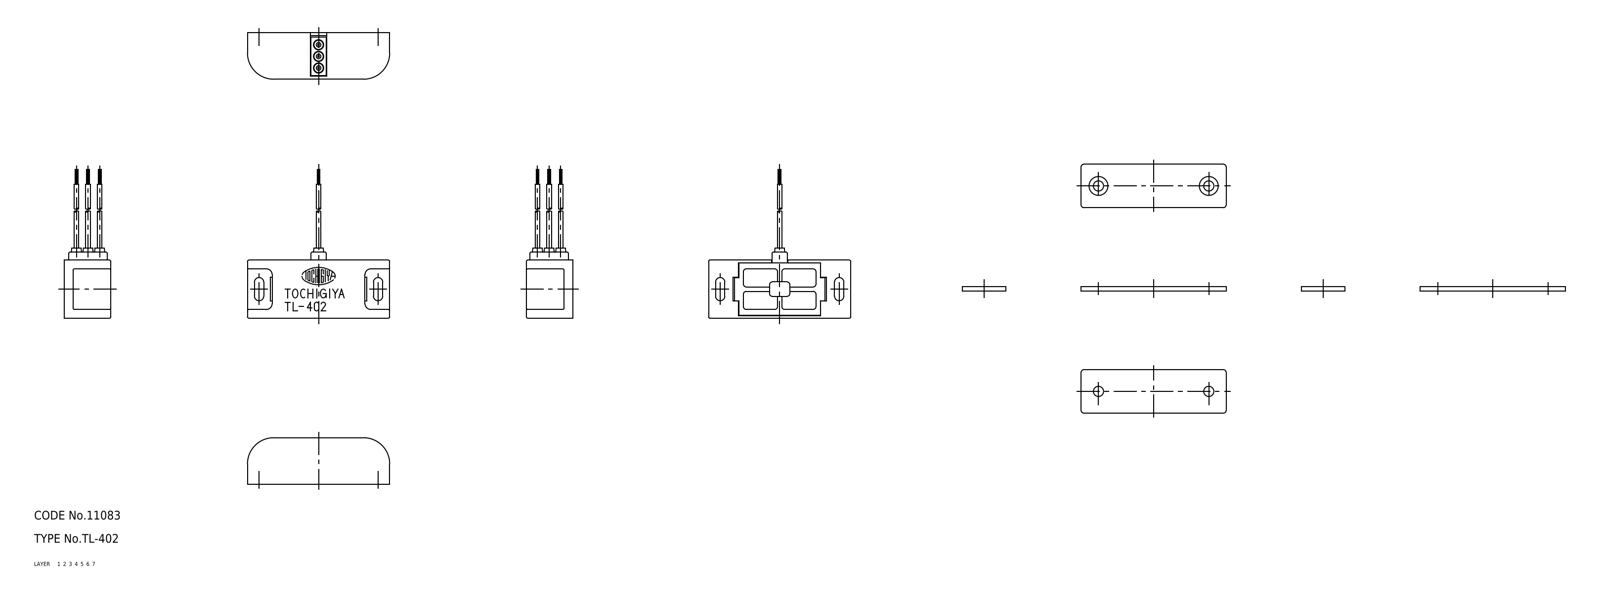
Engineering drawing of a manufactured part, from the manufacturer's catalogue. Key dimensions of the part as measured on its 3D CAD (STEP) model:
Part name (STEP PRODUCT): housing; TL_402; keeper; switch
STEP written by: SolidWorks 2015 (AUTOMOTIVE_DESIGN)
Units: millimetres
Bodies: 3 solids, 211 faces (95 planar, 86 cylindrical, 30 other)
Overall size (bounding box): 70.65 × 50 × 16
Volume: 13 679 mm³ · Surface area: 7 020 mm²
Round bosses / shafts (diameter × count): ⌀0.2 ×21, ⌀1.6 ×3
Partial cylindrical surfaces — rounded edges, fillets, slot ends (radius × count): R0.5 ×18, R1 ×4, R1.6 ×4, R2 ×4, R9 ×2
Main face-to-face distances: 15, 16, 1.5, 16.5, 20, 35, 36.5, 3, 1, 32
